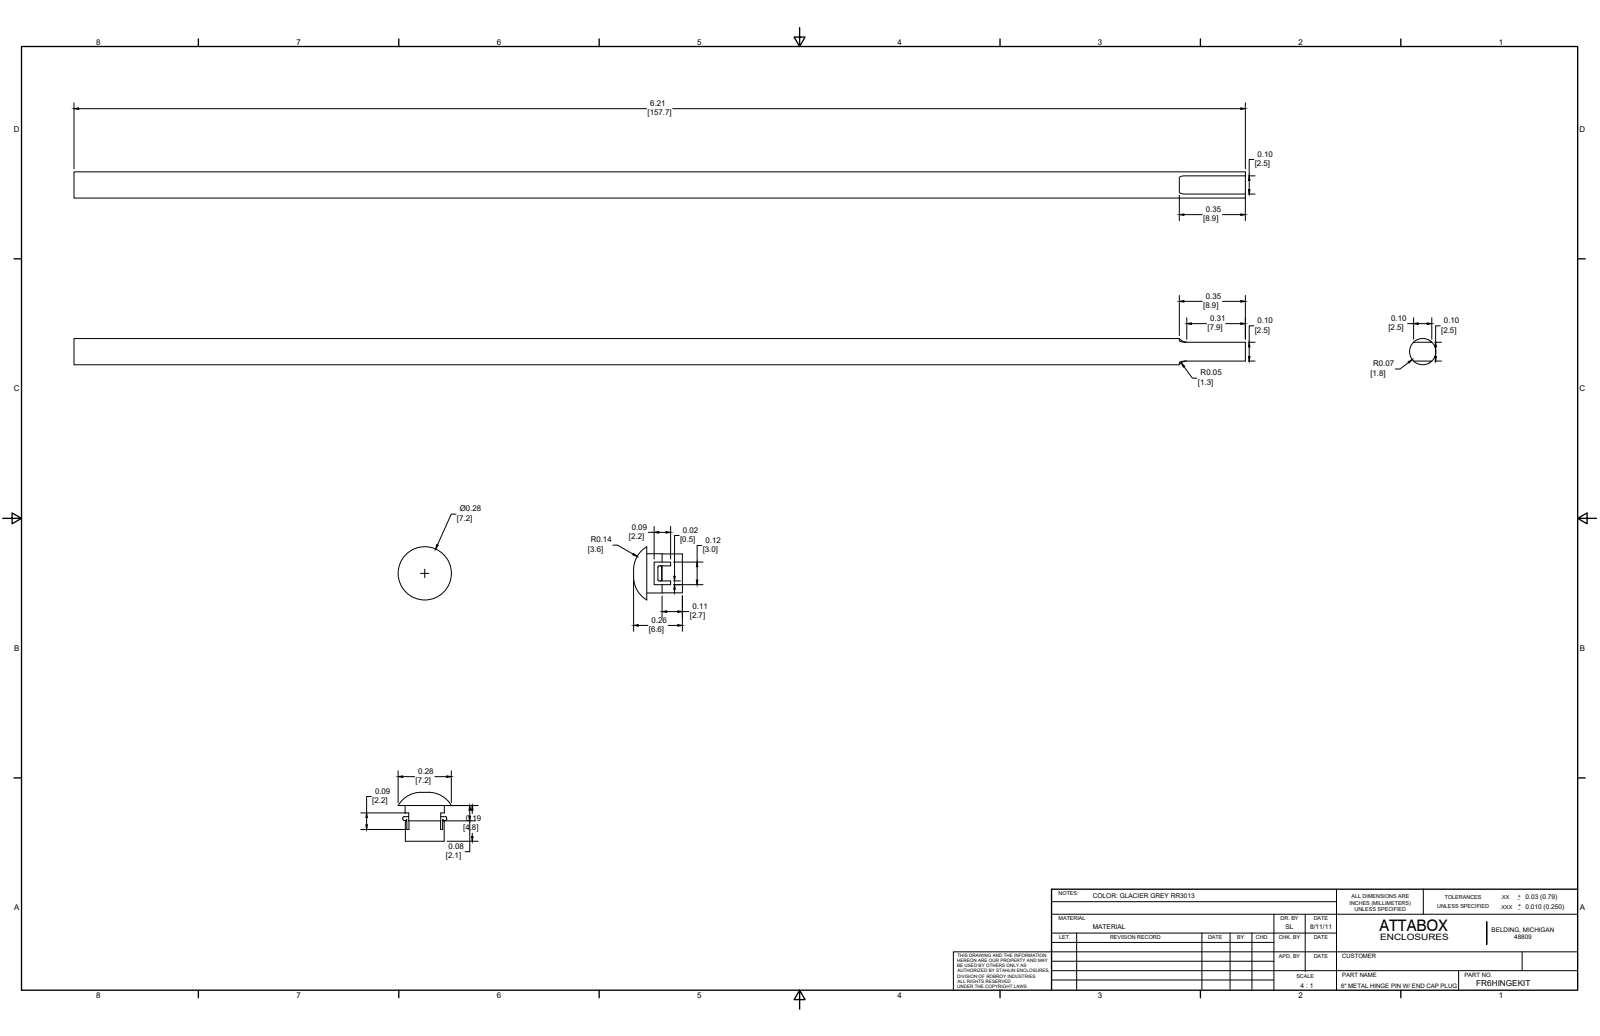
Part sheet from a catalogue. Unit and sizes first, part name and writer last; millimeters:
Units: millimetres
Overall size (bounding box): 162.1 × 60 × 35.3
Round holes (diameter × count): ⌀3.3 ×4
Round bosses / shafts (diameter × count): ⌀5.3 ×4, ⌀5.2 ×4, ⌀3.4 ×2
Partial cylindrical surfaces — rounded edges, fillets, slot ends (radius × count): R0.2 ×32, R0.2 ×12, R10.2 ×4
Main face-to-face distances: 2.4, 2.4, 4.8, 15.2, 15.1, 12.8, 0.5, 2.5, 3.8, 1
Hole centre spacings: 10.3, 13.3, 21.1, 21.8, 27.8, 38.1
Volume: 3 280 mm³ · Surface area: 4 383 mm²
Bodies: 6 solids, 252 faces (136 planar, 86 cylindrical, 30 other)
Part name (STEP PRODUCT): FR6HINGEKIT
STEP written by: SolidWorks 2019 (AUTOMOTIVE_DESIGN)
